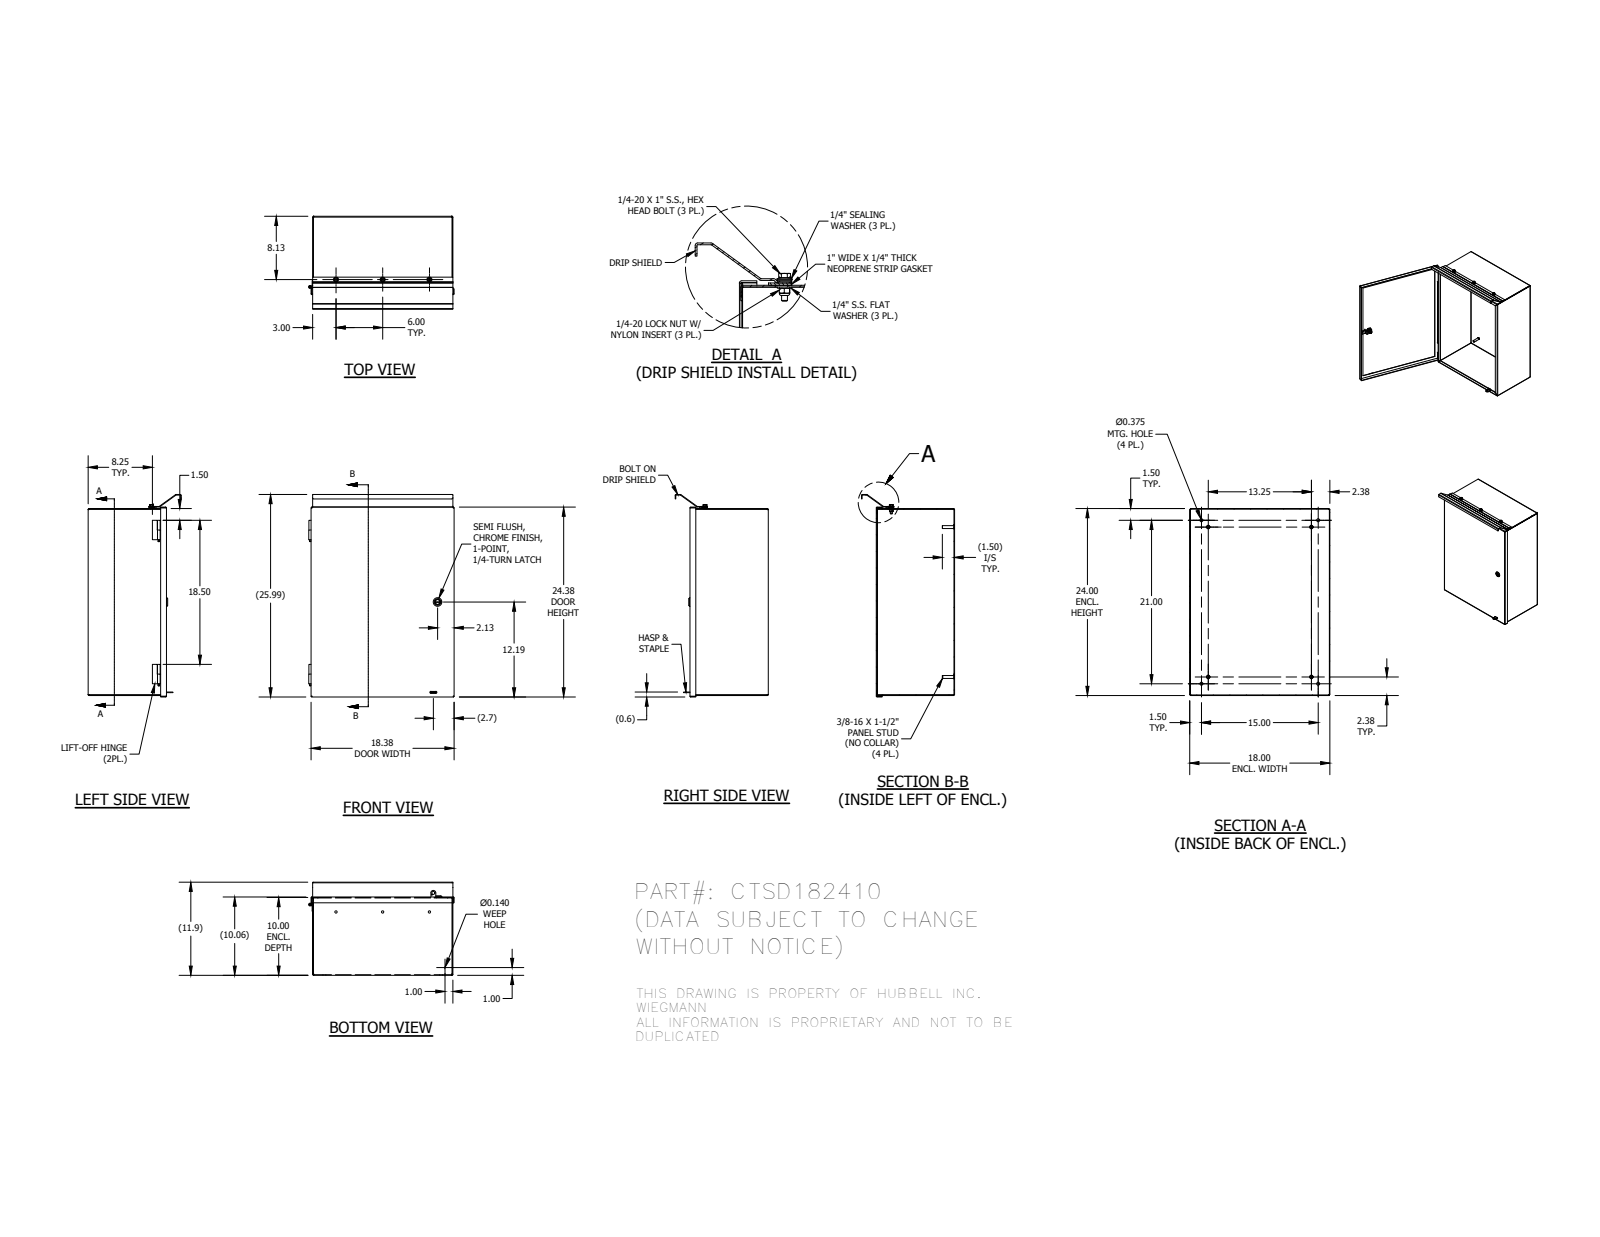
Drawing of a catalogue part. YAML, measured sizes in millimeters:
part_name: "CTSD182410BKP; CTSD1824DR; 31815; HC2527 (+8 more)"
step_written_by: "Autodesk Inventor 2014 (AUTOMOTIVE_DESIGN)"
units: millimeters
bodies: {solids: 36, faces: 860, planar: 456, cylindrical: 259, other: 145}
overall_size: [660.27, 474.07, 303.52]
volume: 2425000
surface_area: 2601000
round_holes:
  - {diameter: 9.52, count: 5}
  - {diameter: 4.98, count: 3}
  - {diameter: 5.97, count: 3}
  - {diameter: 6.99, count: 3}
  - {diameter: 7.14, count: 3}
  - {diameter: 7.37, count: 3}
  - {diameter: 3.17, count: 1}
  - {diameter: 3.56, count: 1}
  - {diameter: 5, count: 1}
  - {diameter: 5.36, count: 1}
  - {diameter: 5.56, count: 1}
  - {diameter: 8, count: 1}
round_bosses_or_shafts:
  - {diameter: 11.73, count: 4}
  - {diameter: 9.52, count: 4}
  - {diameter: 16.51, count: 3}
  - {diameter: 15.88, count: 3}
  - {diameter: 15.24, count: 3}
  - {diameter: 11.13, count: 3}
  - {diameter: 11.05, count: 3}
  - {diameter: 6.6, count: 3}
partial_cylinders:
  - {radius: 0.3, count: 30}
  - {radius: 0.79, count: 20}
  - {radius: 2.67, count: 18}
  - {radius: 0.5, count: 10}
  - {radius: 1.78, count: 8}
  - {radius: 3.17, count: 4}
  - {radius: 4, count: 4}
  - {radius: 0.4, count: 3}
face_to_face_distances: [1.88, 253.6, 455.32, 251.72, 255.48, 607.72, 457.2, 453.44, 605.84, 609.6]
hole_center_spacings: [152.4, 266.96, 381, 455.53, 533.4, 655.5, 7.32, 57.12]
